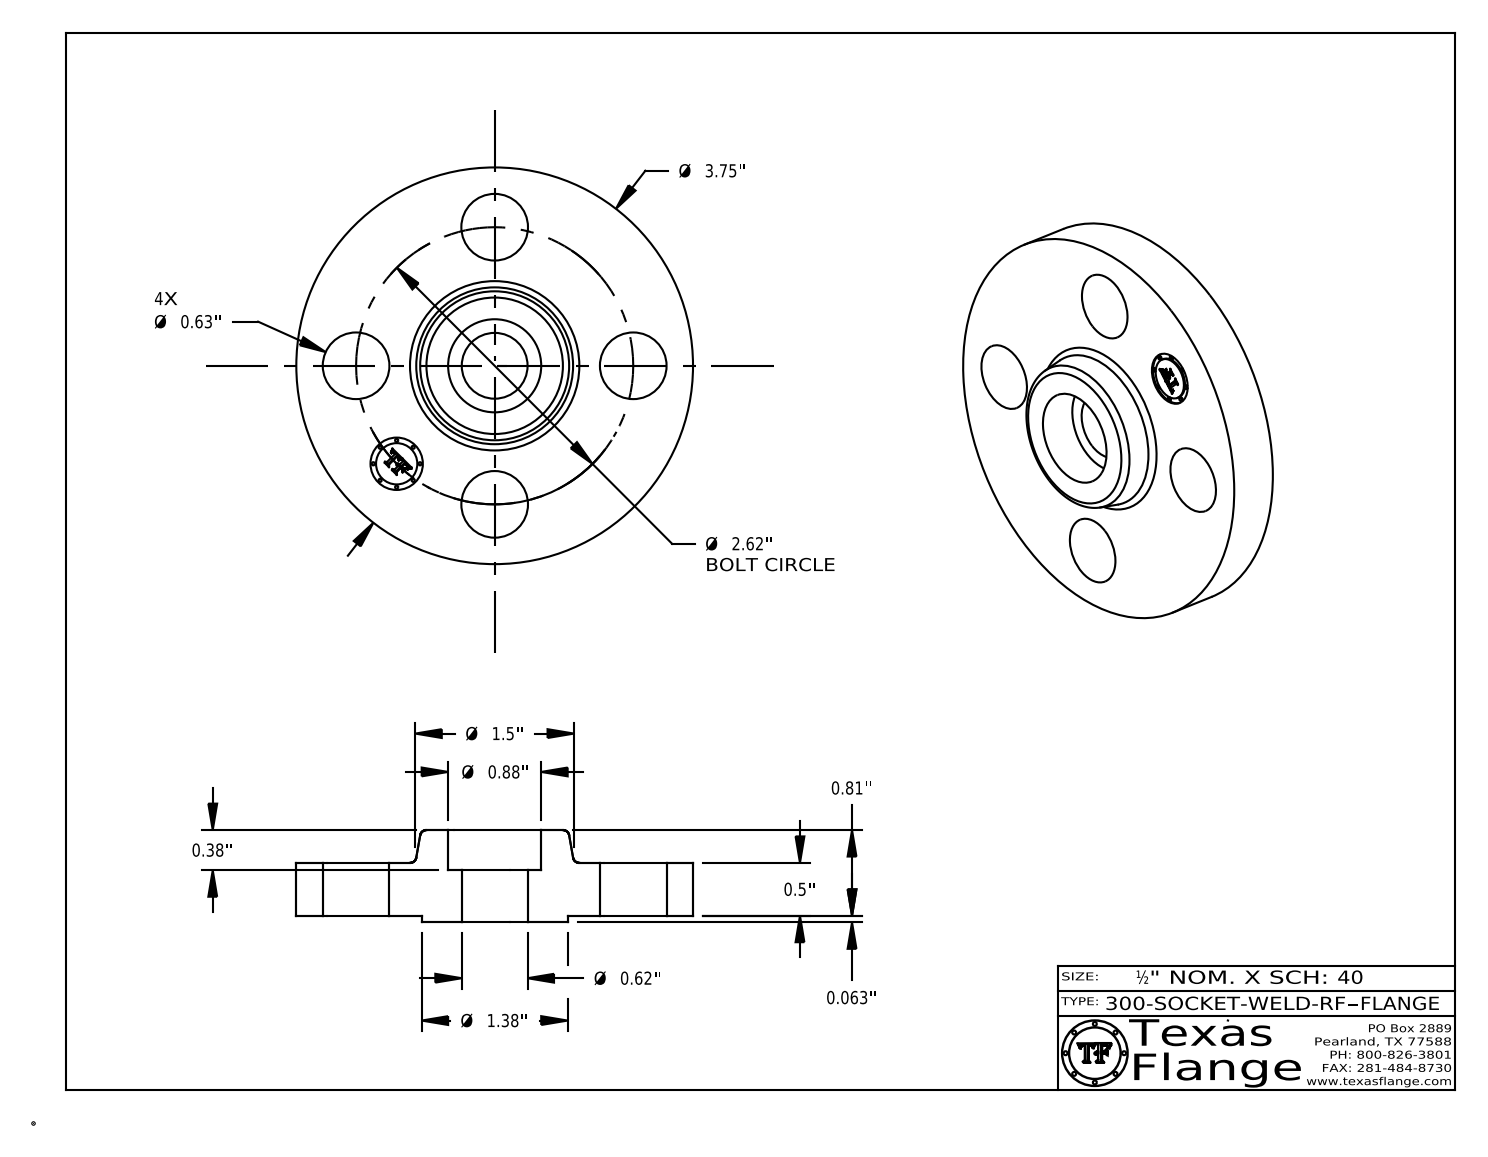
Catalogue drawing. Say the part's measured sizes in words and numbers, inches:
The part is named "300-SOCKET-WELD-RF". Its 3-D file was written by "CATIA V5 STEP AP214 (AUTOMOTIVE_DESIGN)". It is 1 solid with 412 faces: 370 planar, 36 cylindrical and 6 other. Overall it measures 3.75 by 3.75 by 0.873 inches. Its volume is 5.119 cubic inches and its surface area 32.24 square inches. Round holes: 4 of diameter 0.63, 1 of diameter 0.495, 1 of diameter 0.622, 1 of diameter 0.88. Round bosses or shafts: 8 of diameter 0.03, 1 of diameter 3.75, 1 of diameter 1.38, 1 of diameter 0.39. The main face-to-face distances are 0.5, 0.063, 0.563, 0.872, 0.81, 0.31, 0.07, 0.493, 0.43, 0.38. The hole center spacings are 1.31, 1.852, 1.003, 2.42, 2.62, 1.31.
